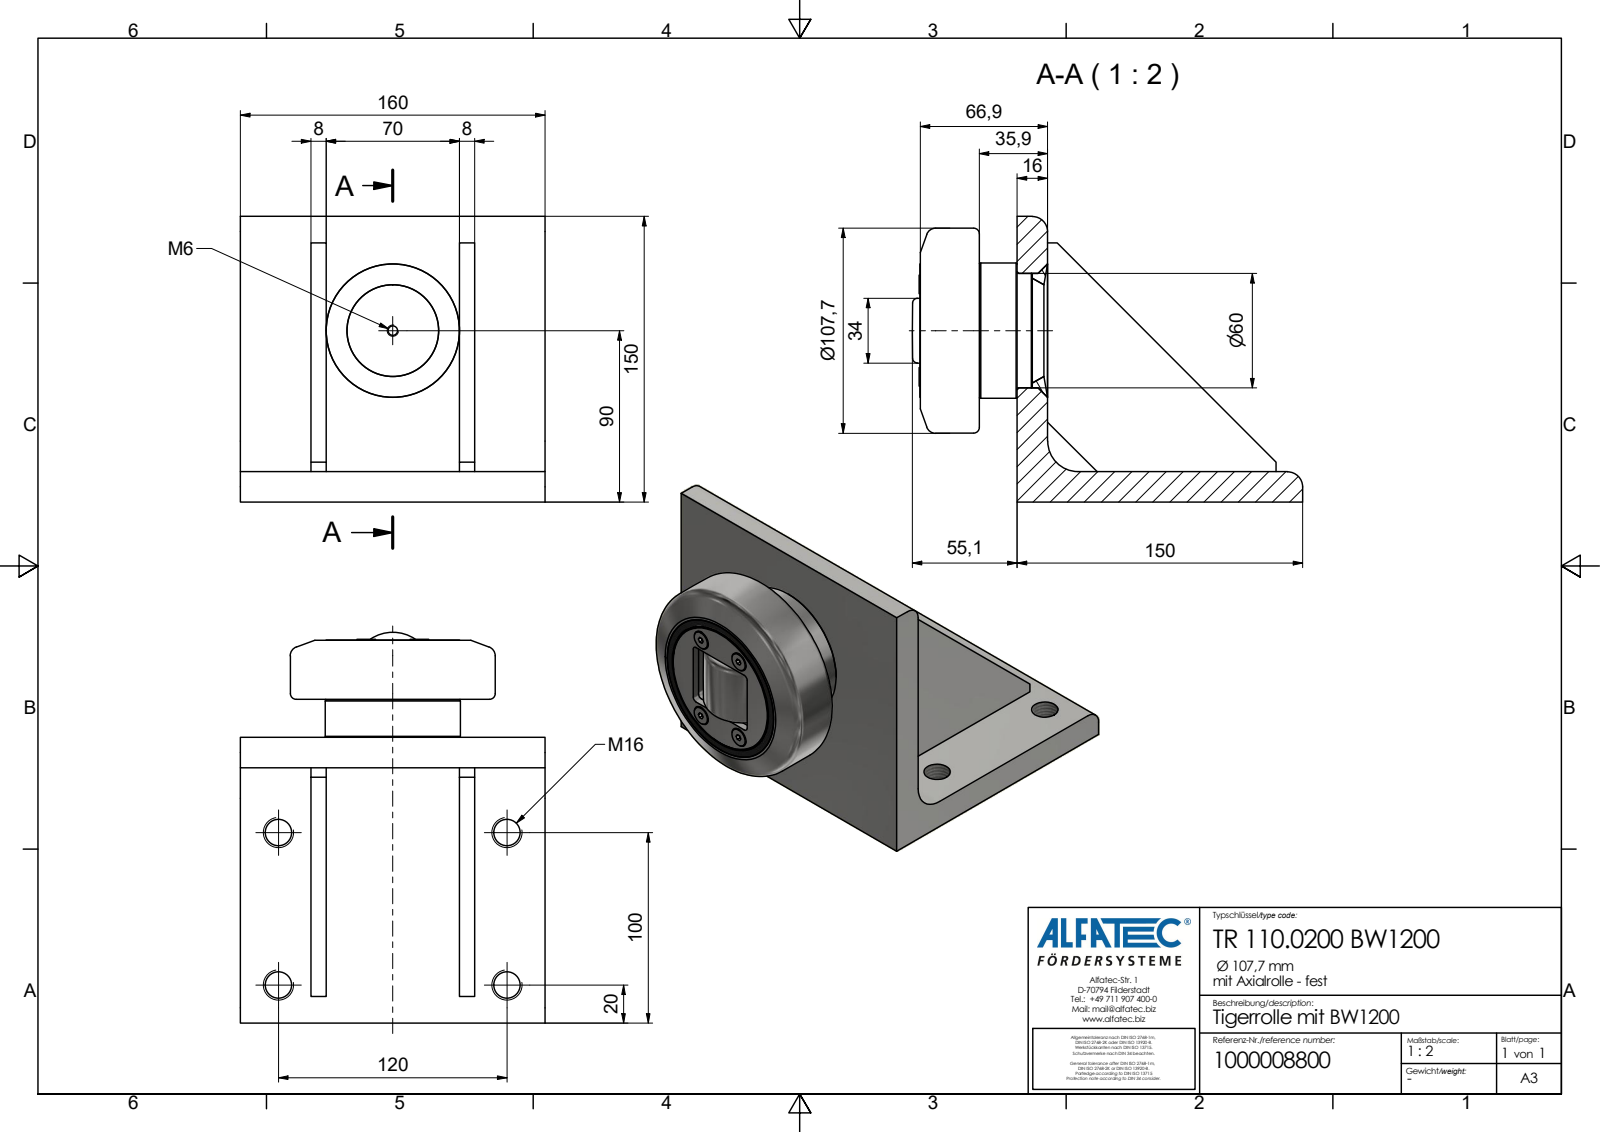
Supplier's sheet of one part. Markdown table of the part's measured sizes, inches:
| quantity | value |
| --- | --- |
| part name | TR 110.0200 BW1200_Kontur |
| STEP written by | Autodesk Inventor 2020 (AP242_MANAGED_MODEL_BASED_3D_ENGINEERING_MIM_LF) |
| units | inches |
| bodies | 1 solid, 98 faces (67 planar, 17 cylindrical, 14 other) |
| overall size | 8.075 × 6.299 × 5.906 |
| volume | 72.86 in³ |
| surface area | 245.5 in² |
| round holes (diameter × count) | 0.545 × 4 |
| round bosses / shafts (diameter × count) | 0.384 × 4, 2.795 × 1, 2.776 × 1 |
| partial cylindrical surfaces (radius × count) | 0.079 × 4, 0.315 × 2, 0.63 × 1 |
| main face-to-face distances | 0.63, 0.315, 3.071, 1.457, 1.772, 4.528, 4.843, 3.386, 2.756, 6.299 |
| hole center spacings | 3.15, 4.724, 5.678 |
